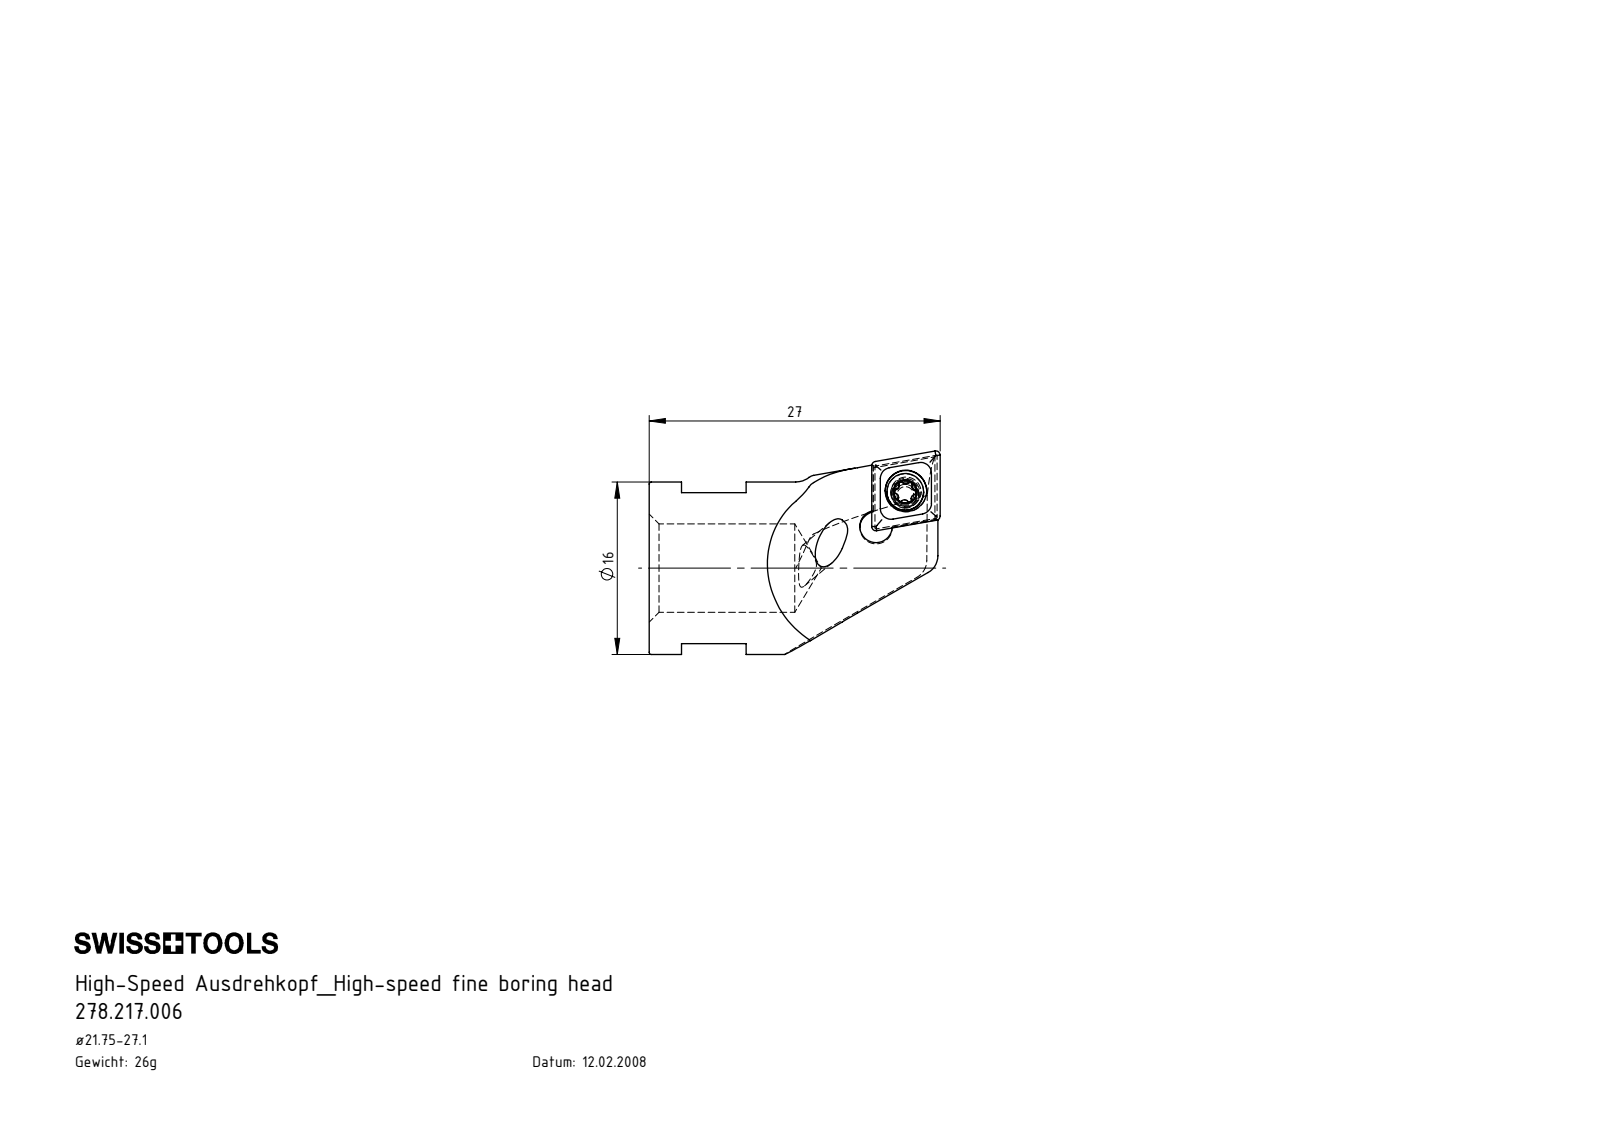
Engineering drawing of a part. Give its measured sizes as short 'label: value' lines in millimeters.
name: HS0-A22.K11.027_A; HS0-A22.K11.027; CCMT060204; WCA-ER2.001.006_A
written by: SolidWorks 2015 (CONFIG_CONTROL_DESIGN)
unit: mm
bodies: 3 solids, 131 faces (39 planar, 40 cylindrical, 52 other)
size: 27 × 18.88 × 16
volume: 3 246 mm³; area: 2 137 mm²
holes: 1× ⌀2.05, 1× ⌀2.8, 1× ⌀3, 1× ⌀3.85, 1× ⌀8.2
bosses: 1× ⌀16, 1× ⌀3.4, 1× ⌀2.5
rounds: 6× R0.21, 5× R0.36, 4× R1, 1× R0.36, 1× R1.5, 1× R1.8, 1× R2
face distances: 2.29, 14.01, 6, 2.38, 9, 3, 2.49, 2.58, 20.8, 17.8
